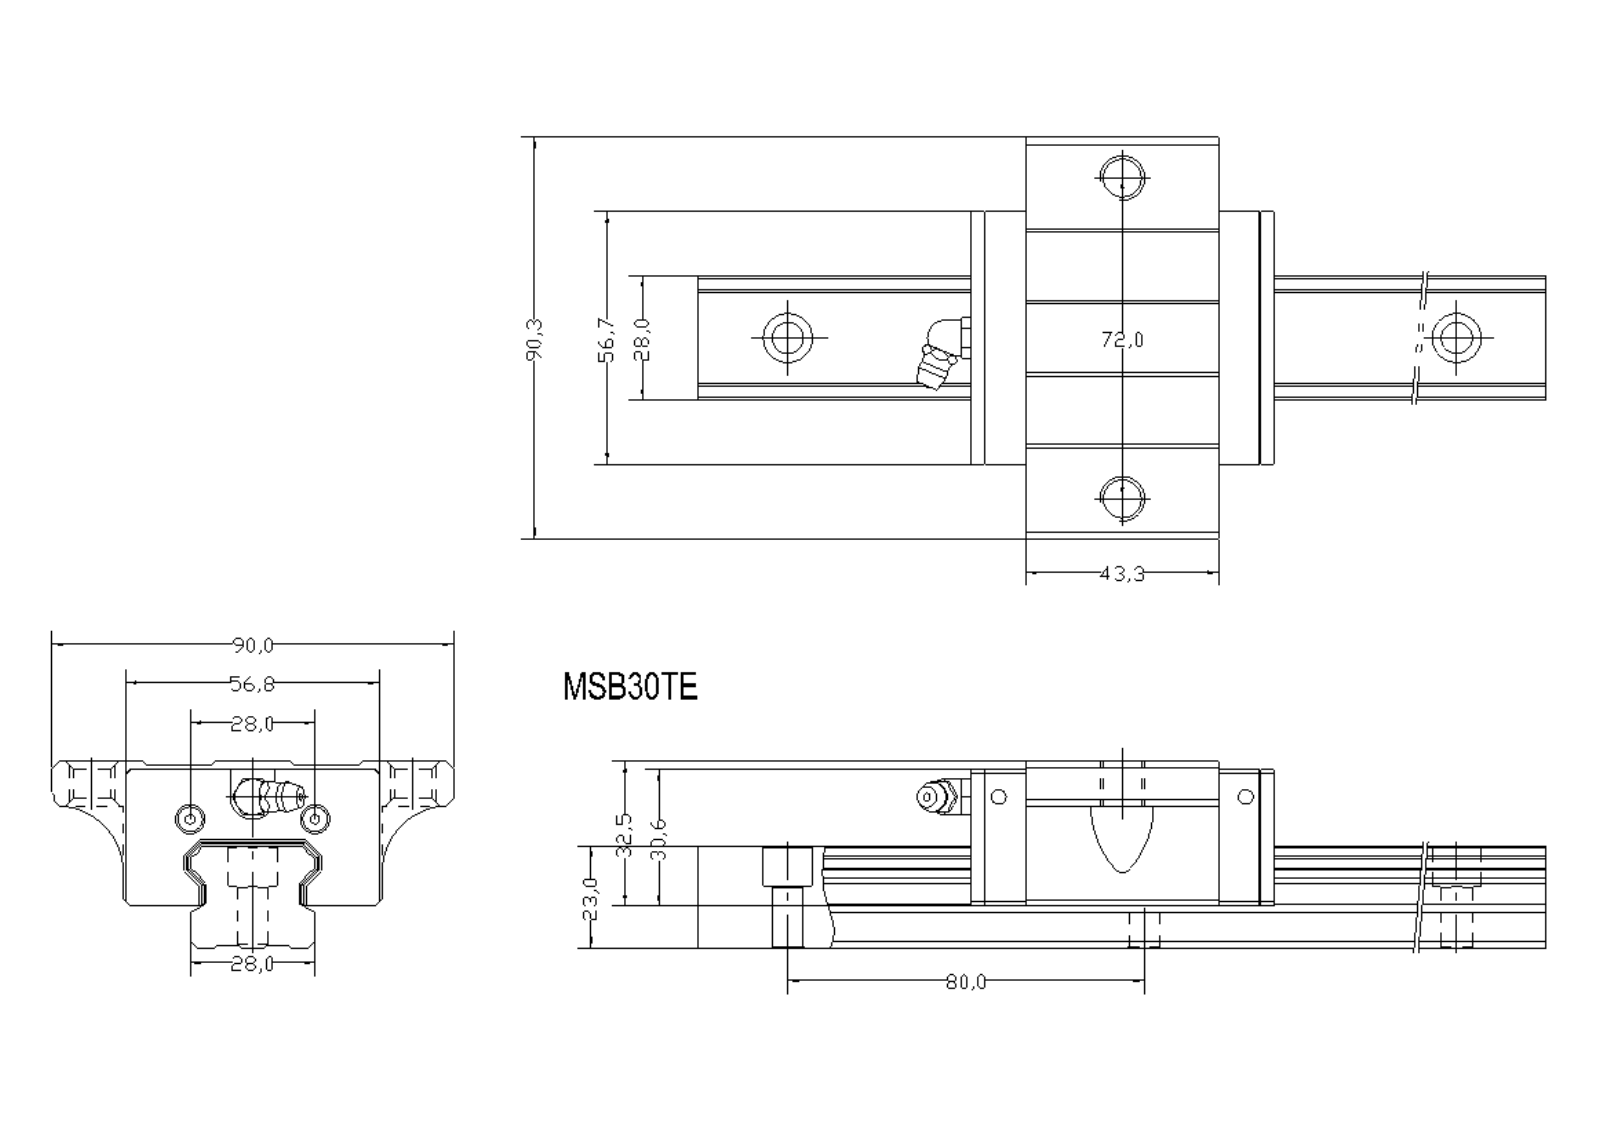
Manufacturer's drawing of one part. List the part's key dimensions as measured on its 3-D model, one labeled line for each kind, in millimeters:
STEP written by: Kubotek KeyCreator V6.5.2 (0407) (CONFIG_CONTROL_DESIGN)
Units: millimetres
Bodies: 3 solids, 212 faces (141 planar, 54 cylindrical, 17 other)
Overall size (bounding box): 280 × 90 × 42
Volume: 269 464 mm³ · Surface area: 55 638 mm²
Round holes (diameter × count): ⌀7 ×4, ⌀11 ×4, ⌀6.5 ×3, ⌀10 ×2
Round bosses / shafts (diameter × count): ⌀8 ×1
Partial cylindrical surfaces — rounded edges, fillets, slot ends (radius × count): R2.6 ×4, R7 ×2, R15 ×2, R5.05 ×1
Main face-to-face distances: 23, 3.5, 24.5, 0.6, 22.4, 42, 41.4, 19, 9.5, 8.9
Hole centre spacings: 53.81, 125.28, 80, 14.87, 160, 28, 72, 240
